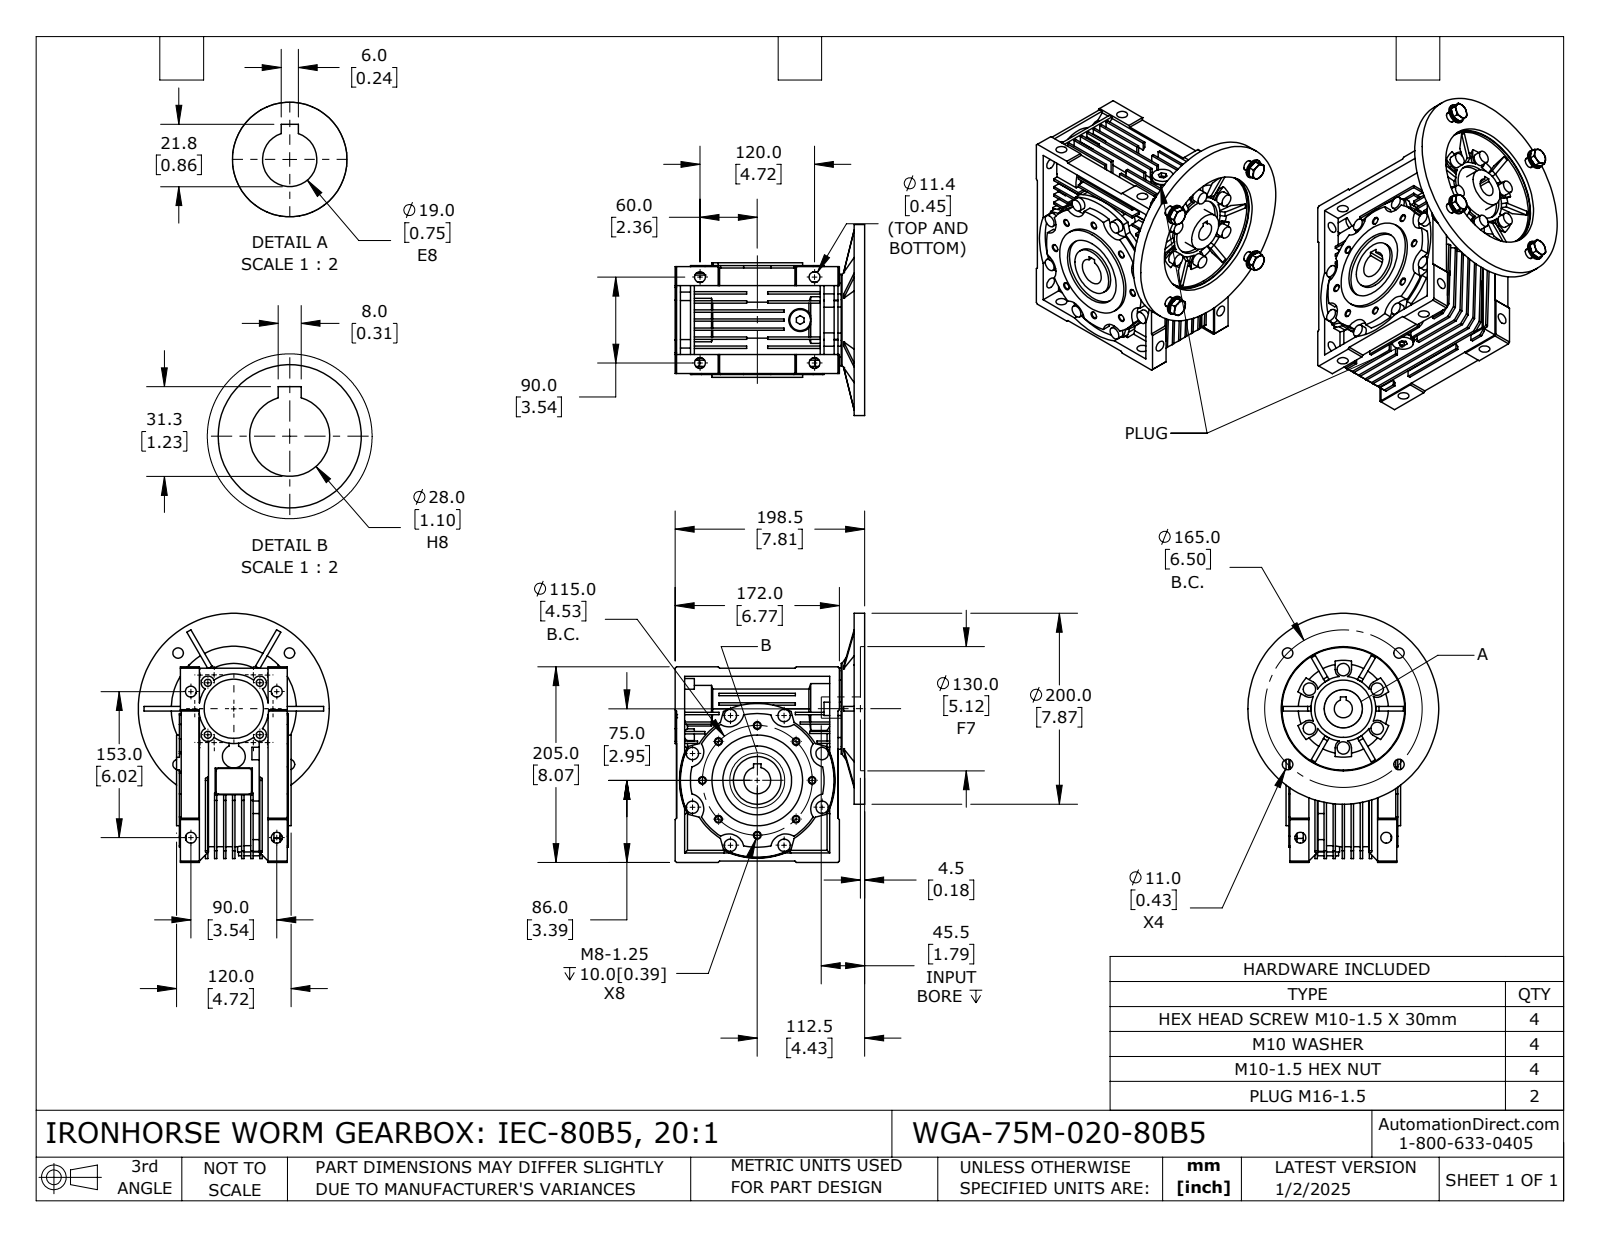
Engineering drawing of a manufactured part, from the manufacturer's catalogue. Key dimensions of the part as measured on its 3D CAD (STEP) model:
Part name (STEP PRODUCT): WGA-75M-020-80B5
STEP written by: SolidWorks 2024 (CONFIG_CONTROL_DESIGN)
Units: millimetres
Bodies: 20 solids, 1447 faces (790 planar, 439 cylindrical, 218 other)
Overall size (bounding box): 261 × 214.93 × 200
Volume: 3 051 000 mm³ · Surface area: 536 406 mm²
Round holes (diameter × count): ⌀6.65 ×8, ⌀11.38 ×8, ⌀7.45 ×4, ⌀8.5 ×4, ⌀10 ×4, ⌀10.5 ×4, ⌀11 ×4, ⌀14.5 ×2, ⌀19 ×1, ⌀20 ×1, ⌀28 ×1, ⌀39 ×1
Round bosses / shafts (diameter × count): ⌀13 ×14, ⌀20 ×4, ⌀16 ×4, ⌀24 ×3, ⌀95 ×2, ⌀22 ×2, ⌀15.8 ×2, ⌀13.7 ×2
Partial cylindrical surfaces — rounded edges, fillets, slot ends (radius × count): R7 ×10, R16 ×8, R8.5 ×6, R2.5 ×4, R33.99 ×1, R36 ×1, R36.5 ×1, R39 ×1
Main face-to-face distances: 9.5, 2.5, 19, 12, 7, 28.5, 16.5, 10, 27.75, 21.5
Hole centre spacings: 44.01, 57.5, 81.32, 91.04, 106.25, 38.49, 54.44, 82.51
